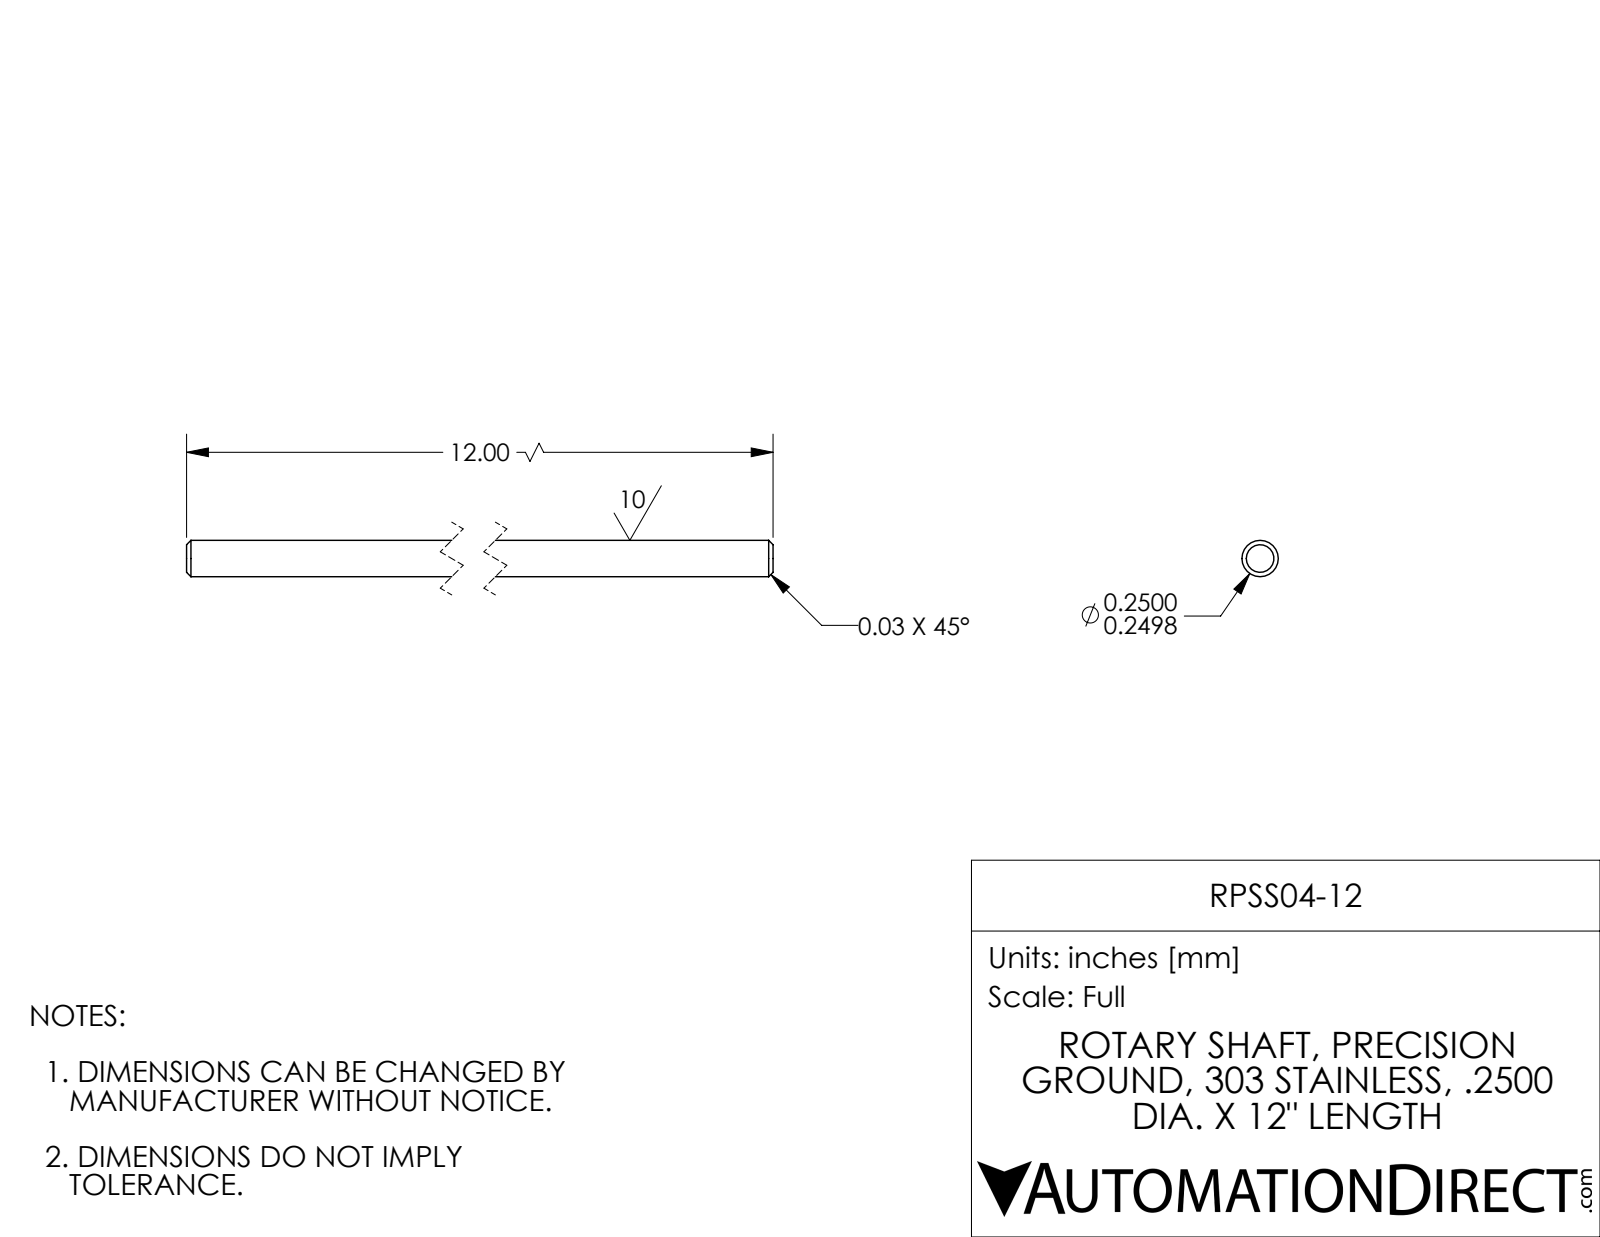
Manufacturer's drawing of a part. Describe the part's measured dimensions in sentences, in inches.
The part is named "RPSS04-12". Its 3-D file was written by "SolidWorks 2017 (AUTOMOTIVE_DESIGN)". It is 1 solid with 8 faces: 2 planar, 2 cylindrical and 4 other. Overall it measures 12 by 0.25 by 0.25 inches. Its volume is 0.588 cubic inches and its surface area 9.493 square inches. Round bosses or shafts: 1 of diameter 0.25. The main face-to-face distances are 12.
